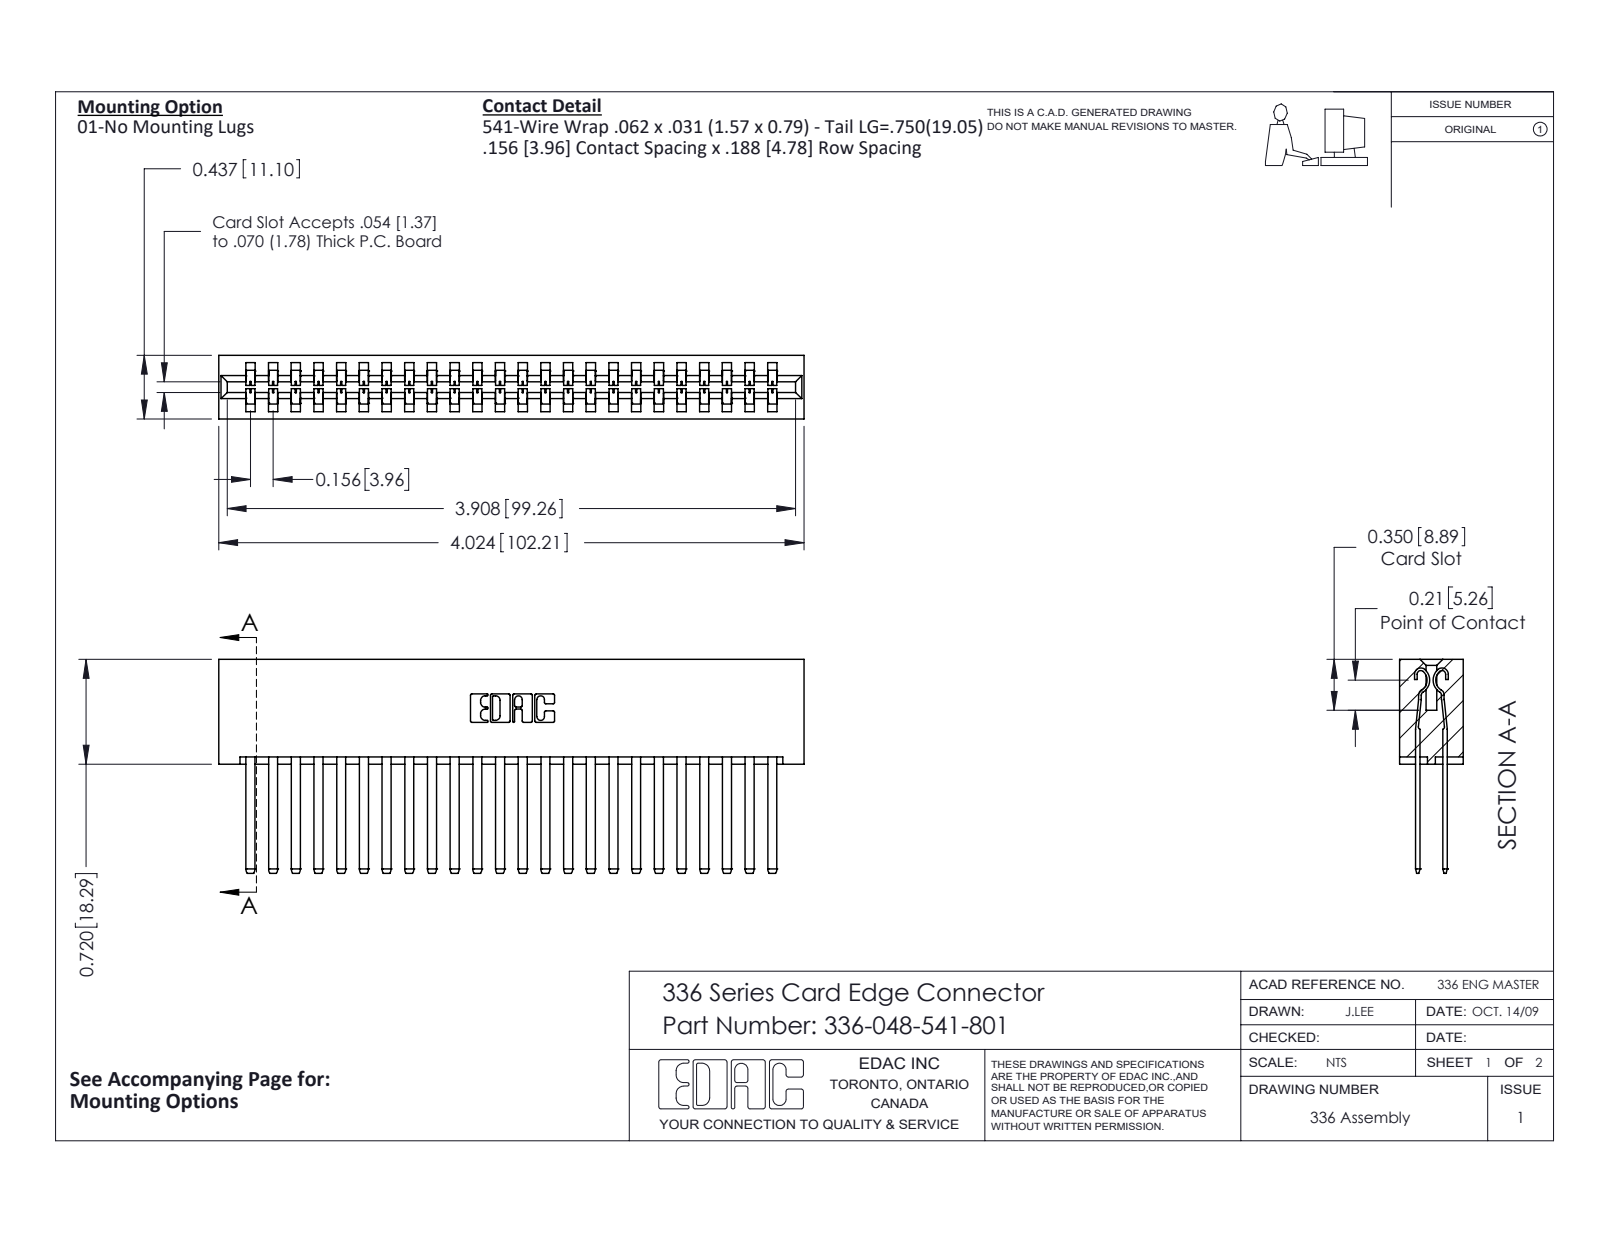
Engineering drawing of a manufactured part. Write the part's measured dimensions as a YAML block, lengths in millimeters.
part_name: "336 Part_Lugless; 336-048-541-801; 336-290-001_336-290-541"
step_written_by: "SolidWorks 2020 (CONFIG_CONTROL_DESIGN)"
units: millimeters
bodies: {solids: 49, faces: 2122, planar: 1314, cylindrical: 808, other: 0}
overall_size: [102.2, 37.3, 11.1]
volume: 16880
surface_area: 21420
partial_cylinders:
  - {radius: 0.1, count: 96}
  - {radius: 1.4, count: 48}
  - {radius: 0.3, count: 22}
  - {radius: 0.2, count: 6}
  - {radius: 0.8, count: 6}
  - {radius: 0.6, count: 4}
  - {radius: 1, count: 4}
  - {radius: 0.7, count: 3}
face_to_face_distances: [4.8, 8.3, 3.6, 7.5, 2.8, 0.8, 11.1, 0.8, 4.6, 4]
